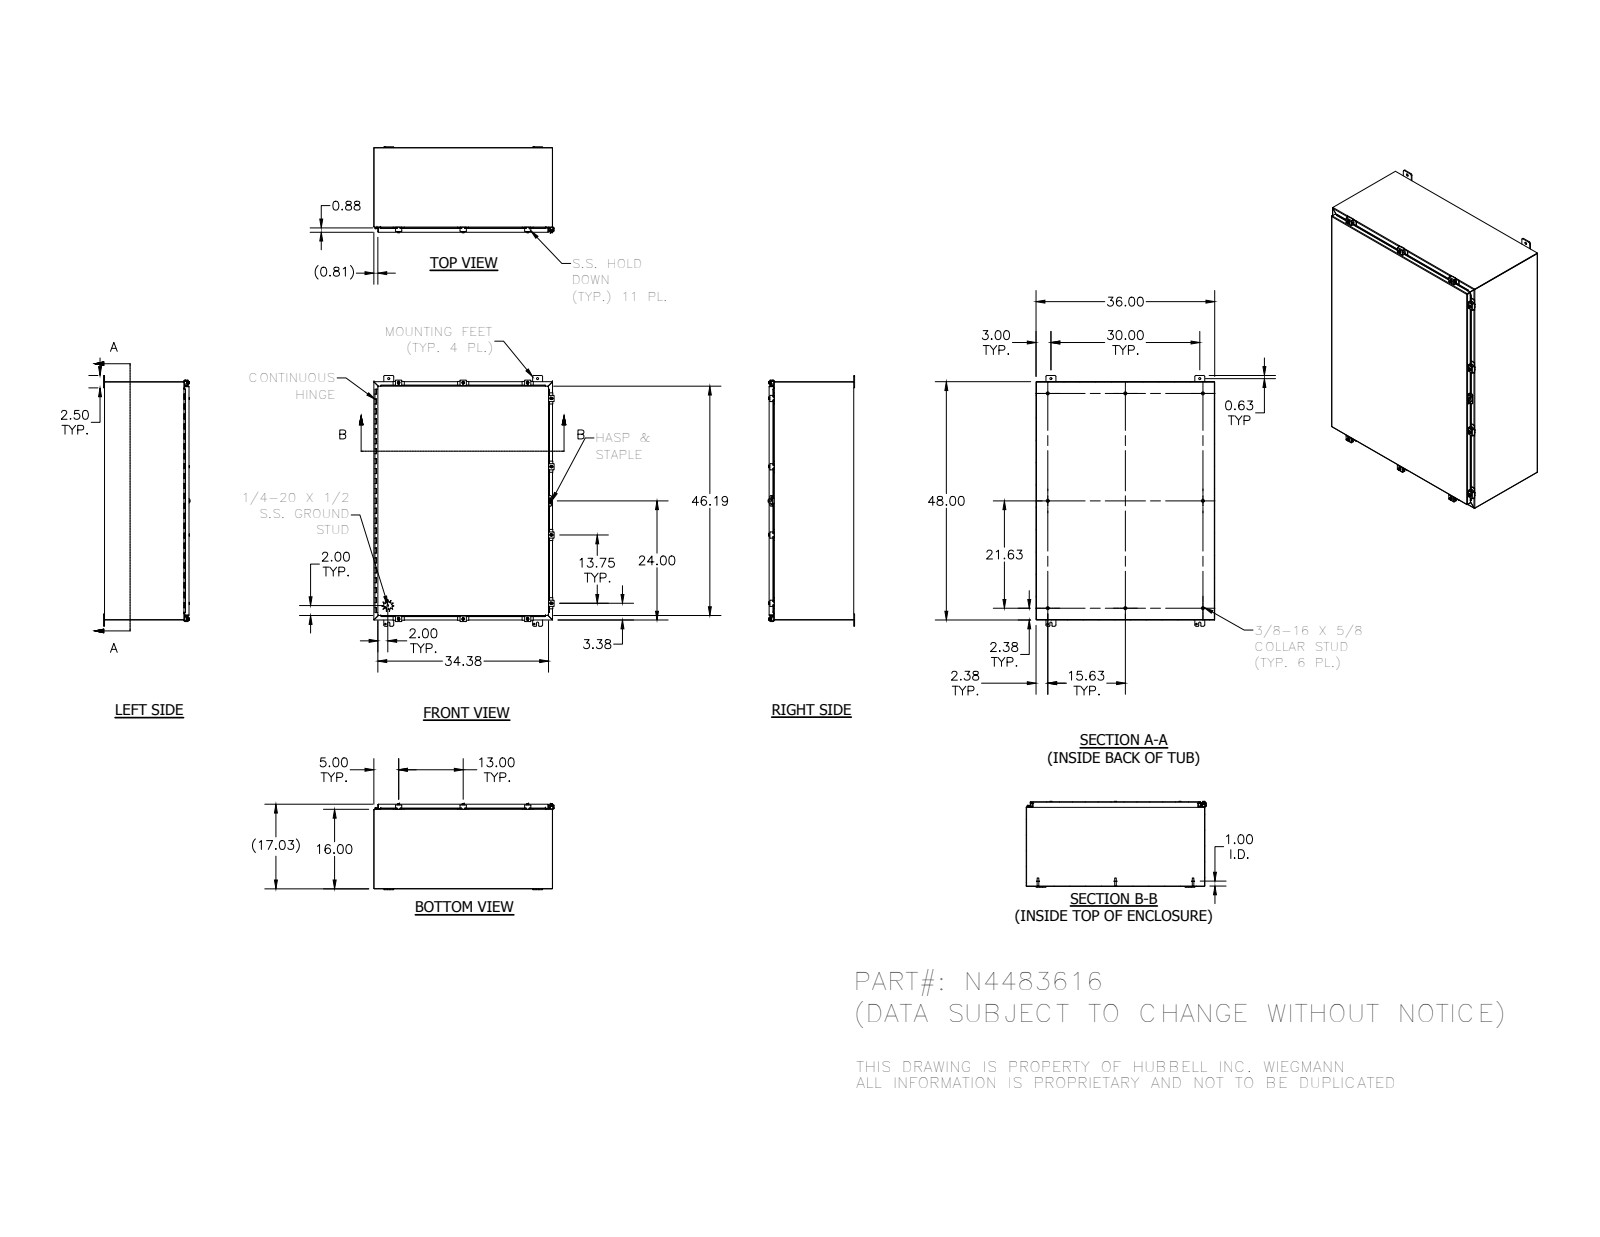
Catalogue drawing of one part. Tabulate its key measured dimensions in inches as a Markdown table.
| quantity | value |
| --- | --- |
| part name | 3293_1; HFW30825-2_1; N4483616BLR_1; 30824_1 (+8 more) |
| STEP written by | SolidWorks 2014 (AUTOMOTIVE_DESIGN) |
| units | inches |
| bodies | 73 solids, 2720 faces (1105 planar, 1190 cylindrical, 425 other) |
| overall size | 50.5 × 36.311 × 17.41 |
| volume | 513.7 in³ |
| surface area | 13 638 in² |
| round holes (diameter × count) | 0.211 × 10, 0.281 × 10, 0.3 × 10, 0.313 × 4, 0.438 × 4, 0.11 × 3, 0.125 × 1, 0.156 × 1, 0.5 × 1 |
| round bosses / shafts (diameter × count) | 0.25 × 12, 0.52 × 10, 0.5 × 10, 0.35 × 10, 0.625 × 8, 0.33 × 8, 0.337 × 1, 0.12 × 1 |
| partial cylindrical surfaces (radius × count) | 0.03 × 117, 0.125 × 41, 0.25 × 37, 0.062 × 22, 0.031 × 21, 0.105 × 21, 0.141 × 20, 0.1 × 14 |
| main face-to-face distances | 0.074, 16.959, 16.885, 17.033, 35.926, 47.926, 35.852, 36, 47.852, 48 |
| hole center spacings | 1.593, 13, 30, 48, 49.36, 56.604, 13.75, 47.617 |
